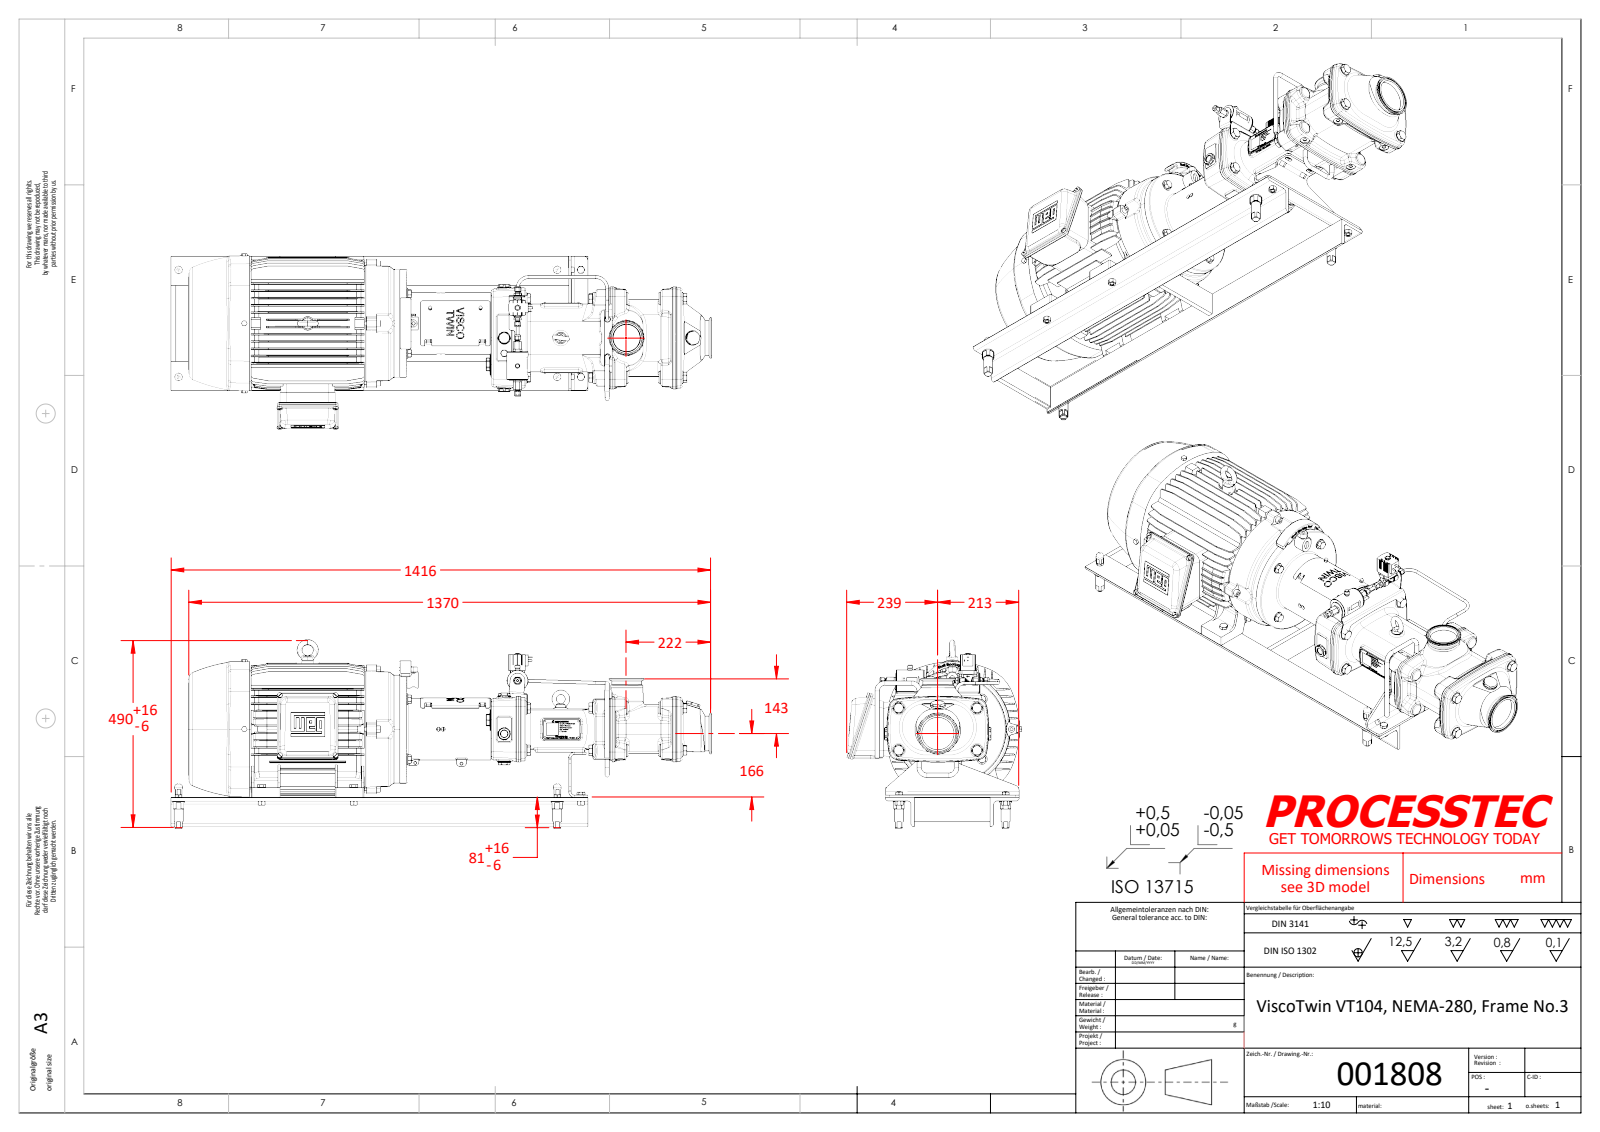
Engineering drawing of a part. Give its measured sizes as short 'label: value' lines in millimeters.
name: Twin Screw Pump VT104 on F3 with NEMA280 - 001808
written by: SolidWorks 2023 (AUTOMOTIVE_DESIGN)
unit: mm
bodies: 124 solids, 13753 faces (5885 planar, 2330 cylindrical, 5538 other)
size: 1415.85 × 490.82 × 458.07
volume: 68 880 000 mm³; area: 4 713 000 mm²
holes: 14× ⌀10.2, 13× ⌀8, 11× ⌀12, 9× ⌀8.5, 8× ⌀6.8, 7× ⌀17, 6× ⌀8.2, 6× ⌀10.5, 6× ⌀13.2, 6× ⌀14.38, 6× ⌀14.5, 5× ⌀4.35
bosses: 12× ⌀8, 12× ⌀6, 9× ⌀10, 8× ⌀30, 8× ⌀24, 8× ⌀19, 8× ⌀12, 8× ⌀5
rounds: 141× R2, 89× R4, 60× R0.5, 60× R5, 56× R3, 54× R8, 39× R1.5, 26× R6
face distances: 9.52, 207.52, 198, 409.64, 189.19, 305, 714.64, 18.67, 132.27, 165.28
hole spacings: 279.4, 51, 158.81, 55, 88.34, 58.87, 62.81, 109.73
